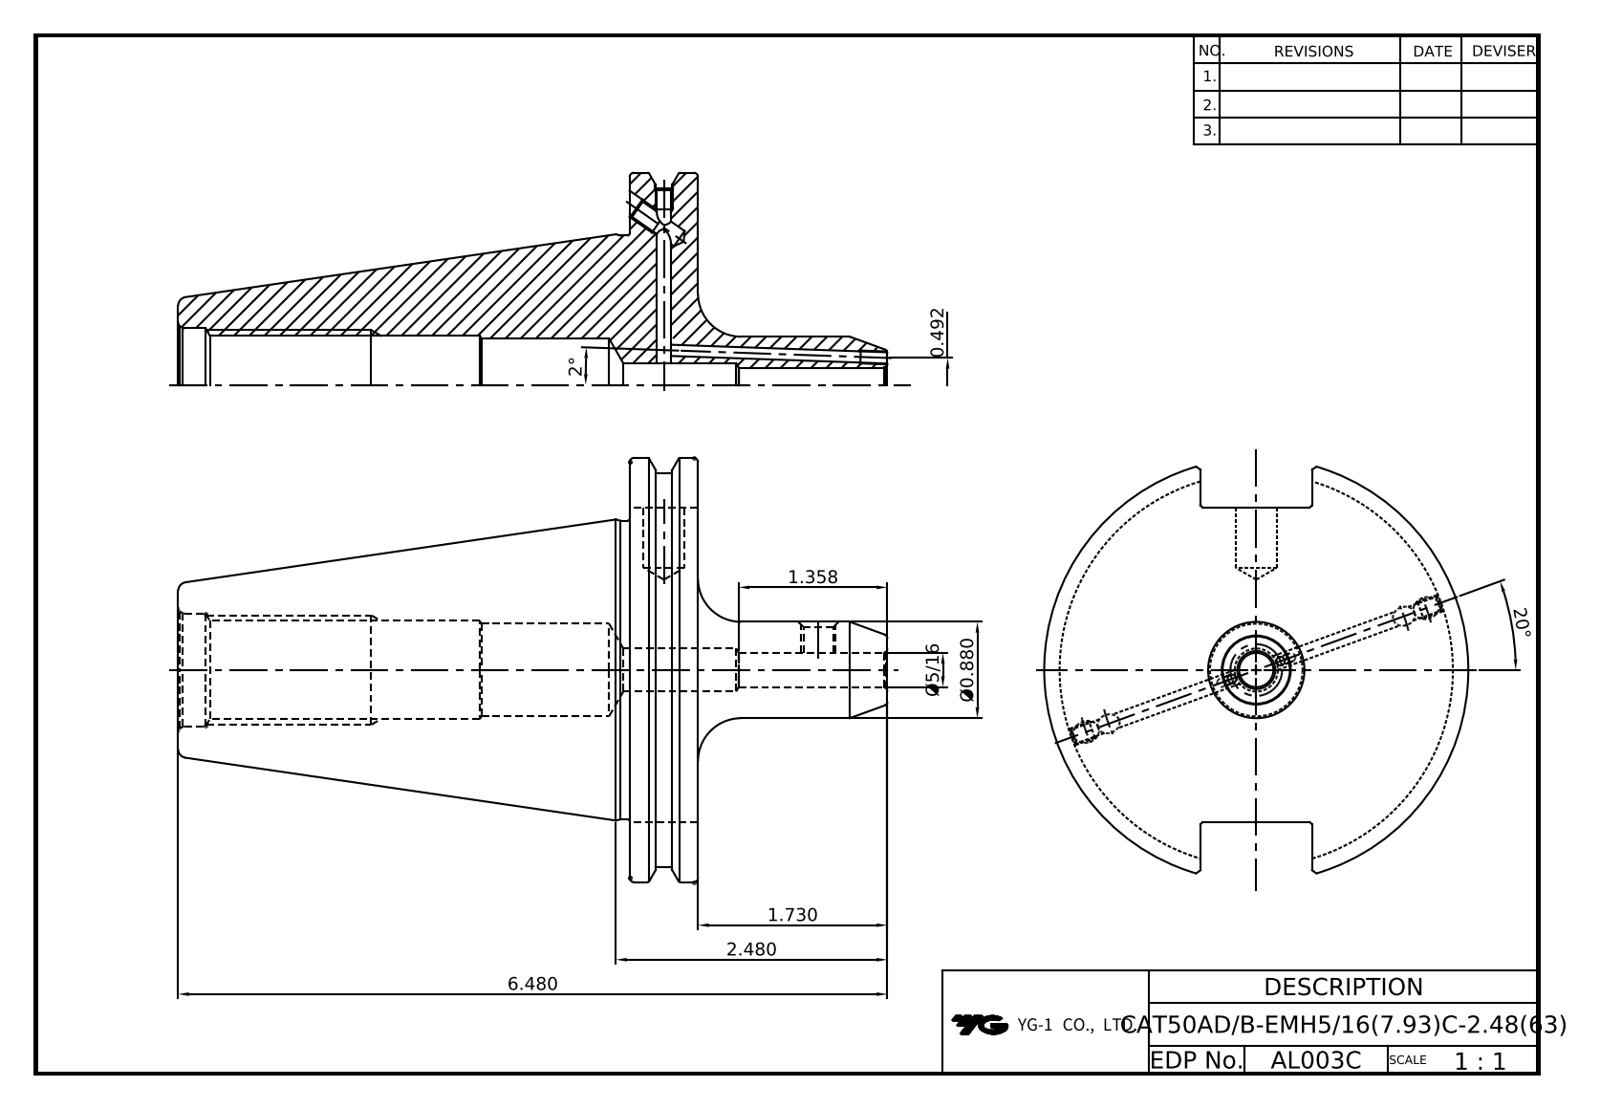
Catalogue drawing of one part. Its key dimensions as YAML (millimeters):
part_name: "LO-CAT50ADB-EMH7.9375C-63"
step_written_by: "Autodesk Inventor 2025 (AUTOMOTIVE_DESIGN)"
units: millimeters
bodies: {solids: 1, faces: 88, planar: 36, cylindrical: 28, other: 24}
overall_size: [164.6, 98.42, 94.69]
volume: 337489
surface_area: 49572
round_holes:
  - {diameter: 2.46, count: 2}
  - {diameter: 3.24, count: 2}
  - {diameter: 4.13, count: 2}
  - {diameter: 4.2, count: 2}
  - {diameter: 5, count: 2}
  - {diameter: 6.78, count: 1}
  - {diameter: 7.94, count: 1}
  - {diameter: 9.53, count: 1}
  - {diameter: 10, count: 1}
  - {diameter: 21.97, count: 1}
  - {diameter: 26.2, count: 1}
round_bosses_or_shafts:
  - {diameter: 98.42, count: 1}
  - {diameter: 91.29, count: 1}
  - {diameter: 69.25, count: 1}
  - {diameter: 22.35, count: 1}
face_to_face_distances: [15.88, 104.77, 120.65, 73.03, 25.9, 114.64, 9.87, 6.01, 110.81, 6.04]
hole_center_spacings: [35.87]
